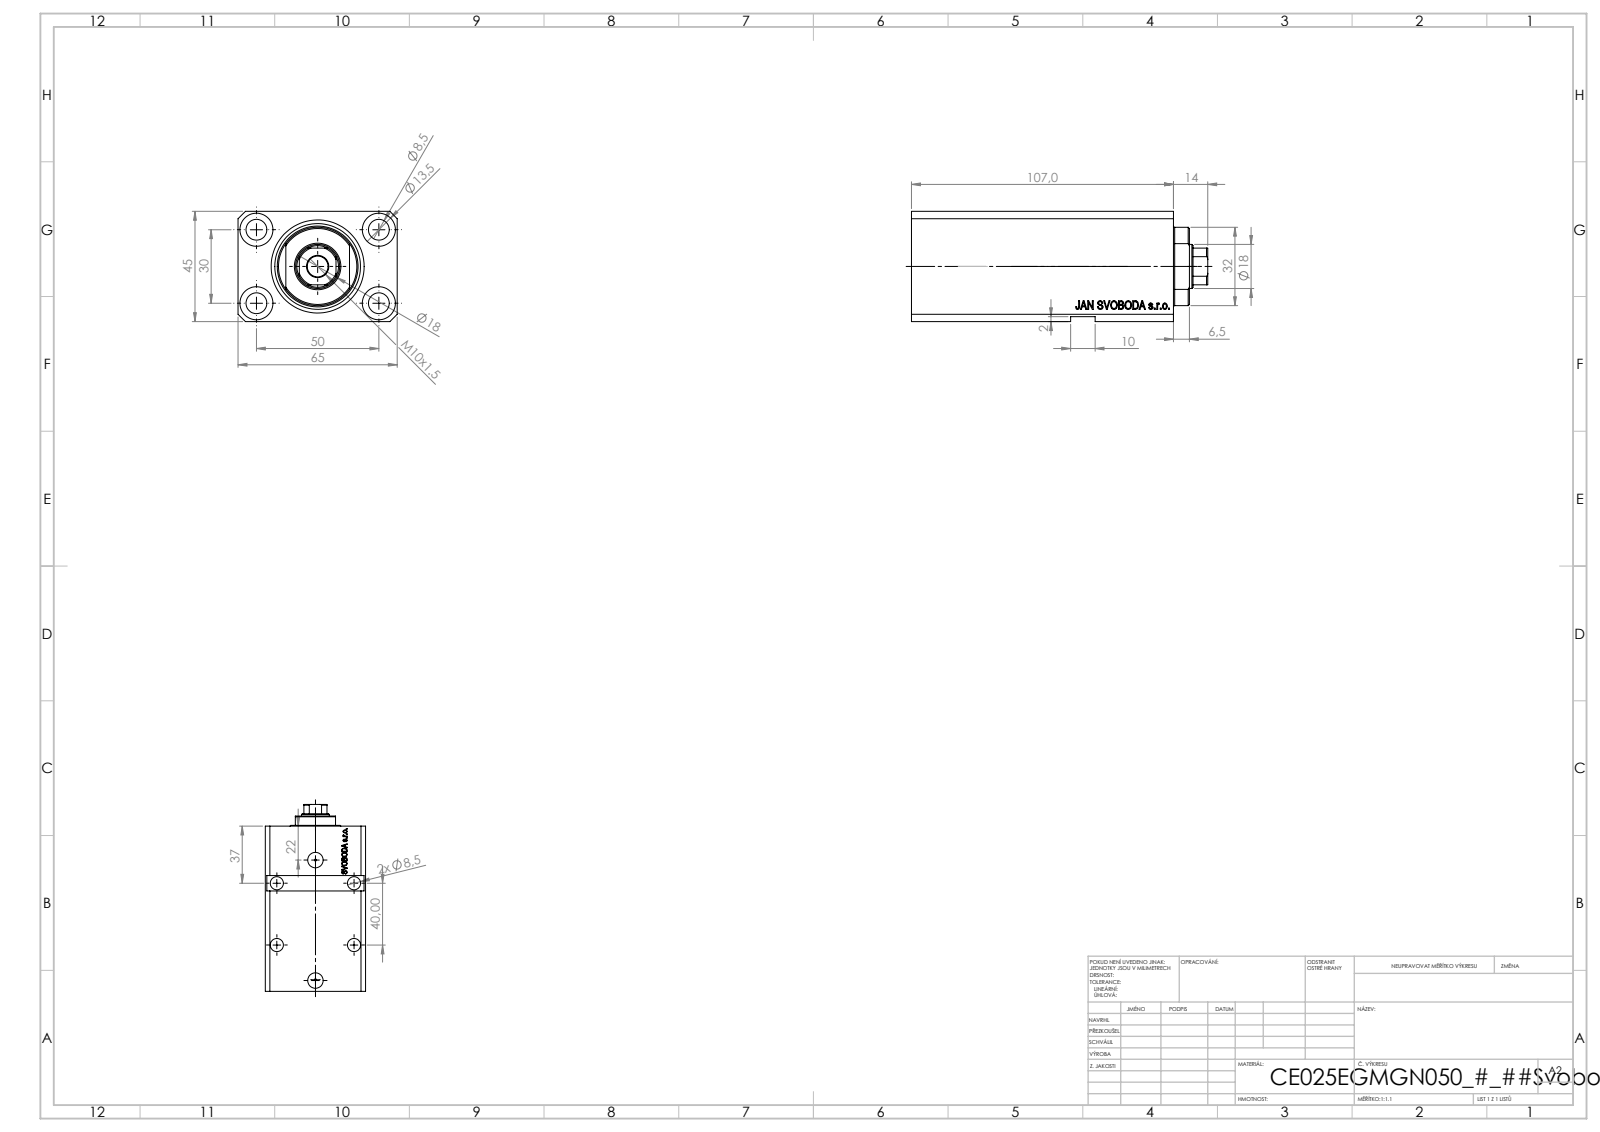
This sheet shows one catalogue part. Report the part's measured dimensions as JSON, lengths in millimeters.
{"part_name": "V250CE_E_Body; V250CE_C_VCP; V250CE_VC_E", "step_written_by": "SolidWorks 2019 (CONFIG_CONTROL_DESIGN)", "units": "millimeters", "bodies": {"solids": 3, "faces": 917, "planar": 435, "cylindrical": 104, "other": 378}, "overall_size": [121, 65, 45], "volume_mm3": 261553, "surface_area_mm2": 66925, "round_holes": [[8.5, 9], [1.25, 4], [13.5, 4], [10, 2], [13.16, 2], [20, 2], [18, 1], [25, 1], [38, 1]], "partial_cylinders_radius": [[8.5, 1], [16, 1]], "face_to_face_distances": [45, 65, 93, 14, 107, 6.9, 86.1, 100.1, 43, 9], "hole_center_spacings": [29.15, 50, 30, 33.61, 33.97, 40, 58.31, 60.42]}
